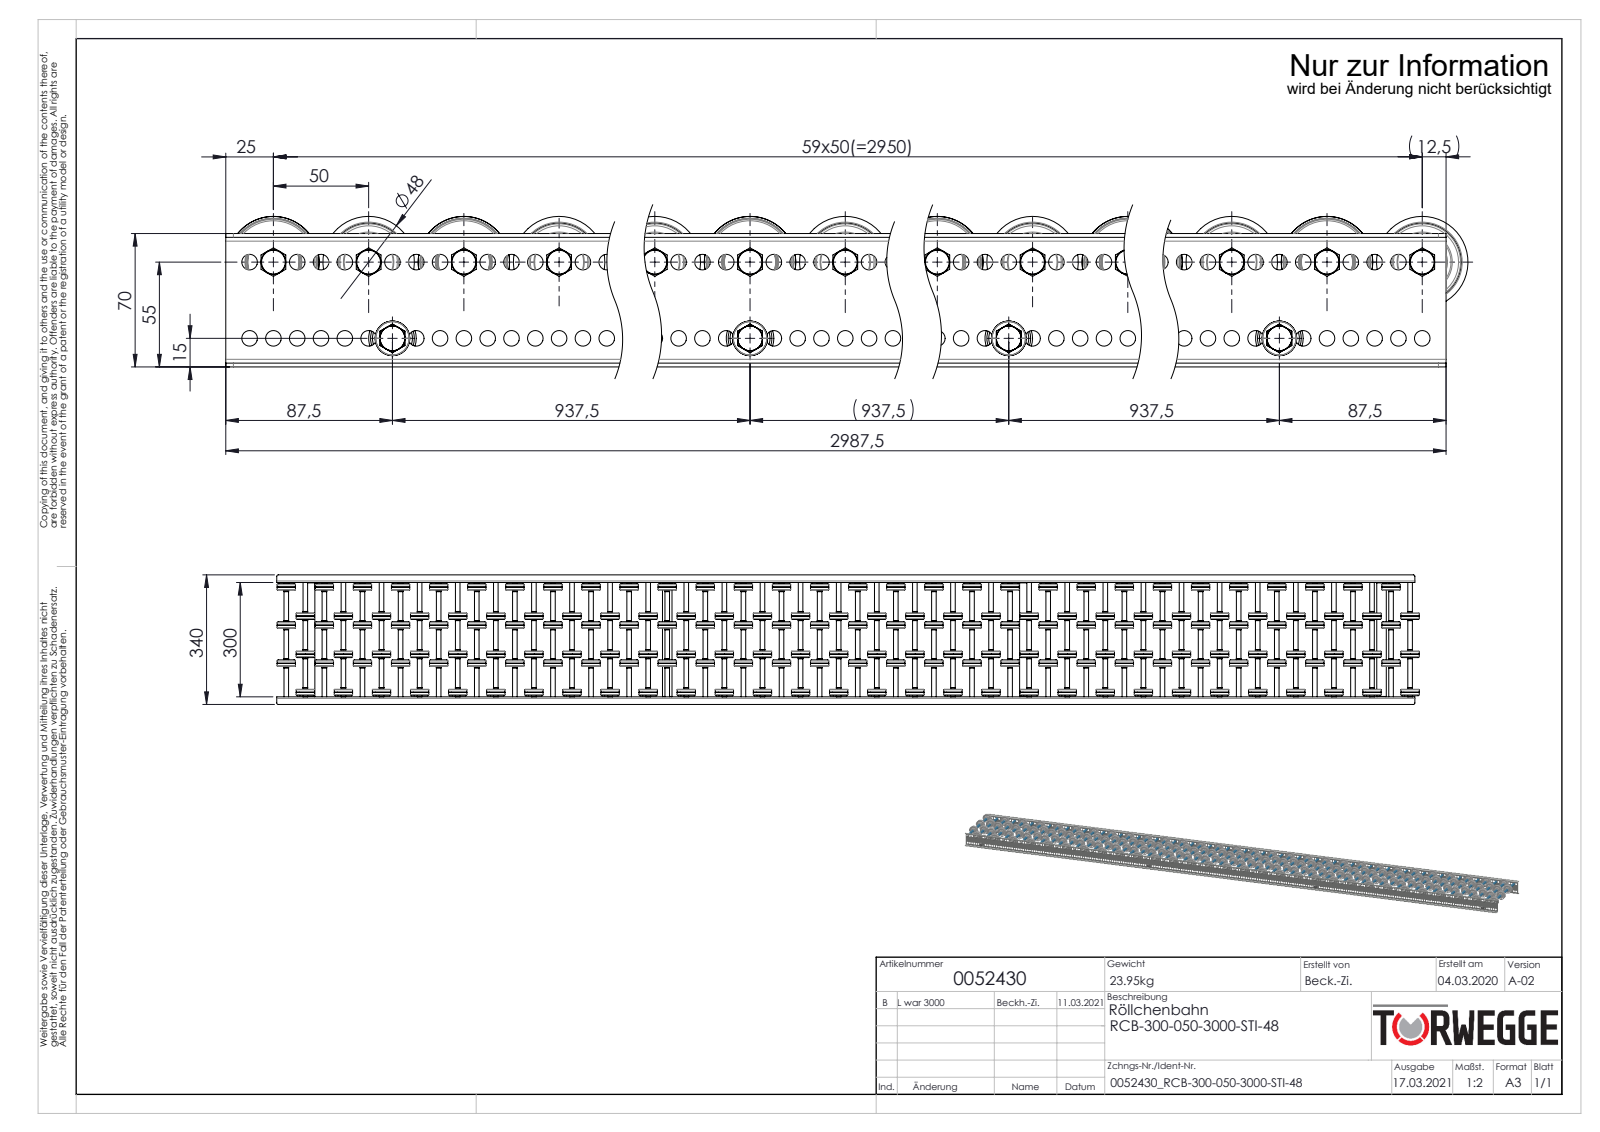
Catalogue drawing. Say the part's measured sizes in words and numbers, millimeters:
The part is named "Traversen_KFG_L300; S100994_Sperrzahnschraube_M08x16-8.8-A2K; Hutmutter_DIN_1587_M8; 0046278_KB-ROHR-12X1,75mm_KFG_L76 (+5 more)". Its 3-D file was written by "SolidWorks 2020 (AUTOMOTIVE_DESIGN)". It is 742 solids with 21732 faces: 4524 planar, 8000 cylindrical and 9208 other. Overall it measures 2999 by 340 by 79 millimeters. Its volume is 6 790 000 cubic millimeters and its surface area 5 162 000 square millimeters. Round holes: 476 of diameter 8.2, 60 of diameter 6.65, 60 of diameter 8, 60 of diameter 9.65, 60 of diameter 15, 60 of diameter 41, 4 of diameter 6.8, 4 of diameter 21. Round bosses or shafts: 60 of diameter 48, 60 of diameter 13, 60 of diameter 12.5, 60 of diameter 12.4, 60 of diameter 12, 60 of diameter 11.5, 4 of diameter 25, 4 of diameter 8. Partial cylindrical surfaces (rounded edges, fillets, slot ends): 8 of radius 4, 4 of radius 2. The main face-to-face distances are 2, 100, 302, 76, 12, 88, 200, 112, 188, 14. The hole center spacings are 12.5, 25, 37.5, 50, 62.5, 75, 87.5, 100.
